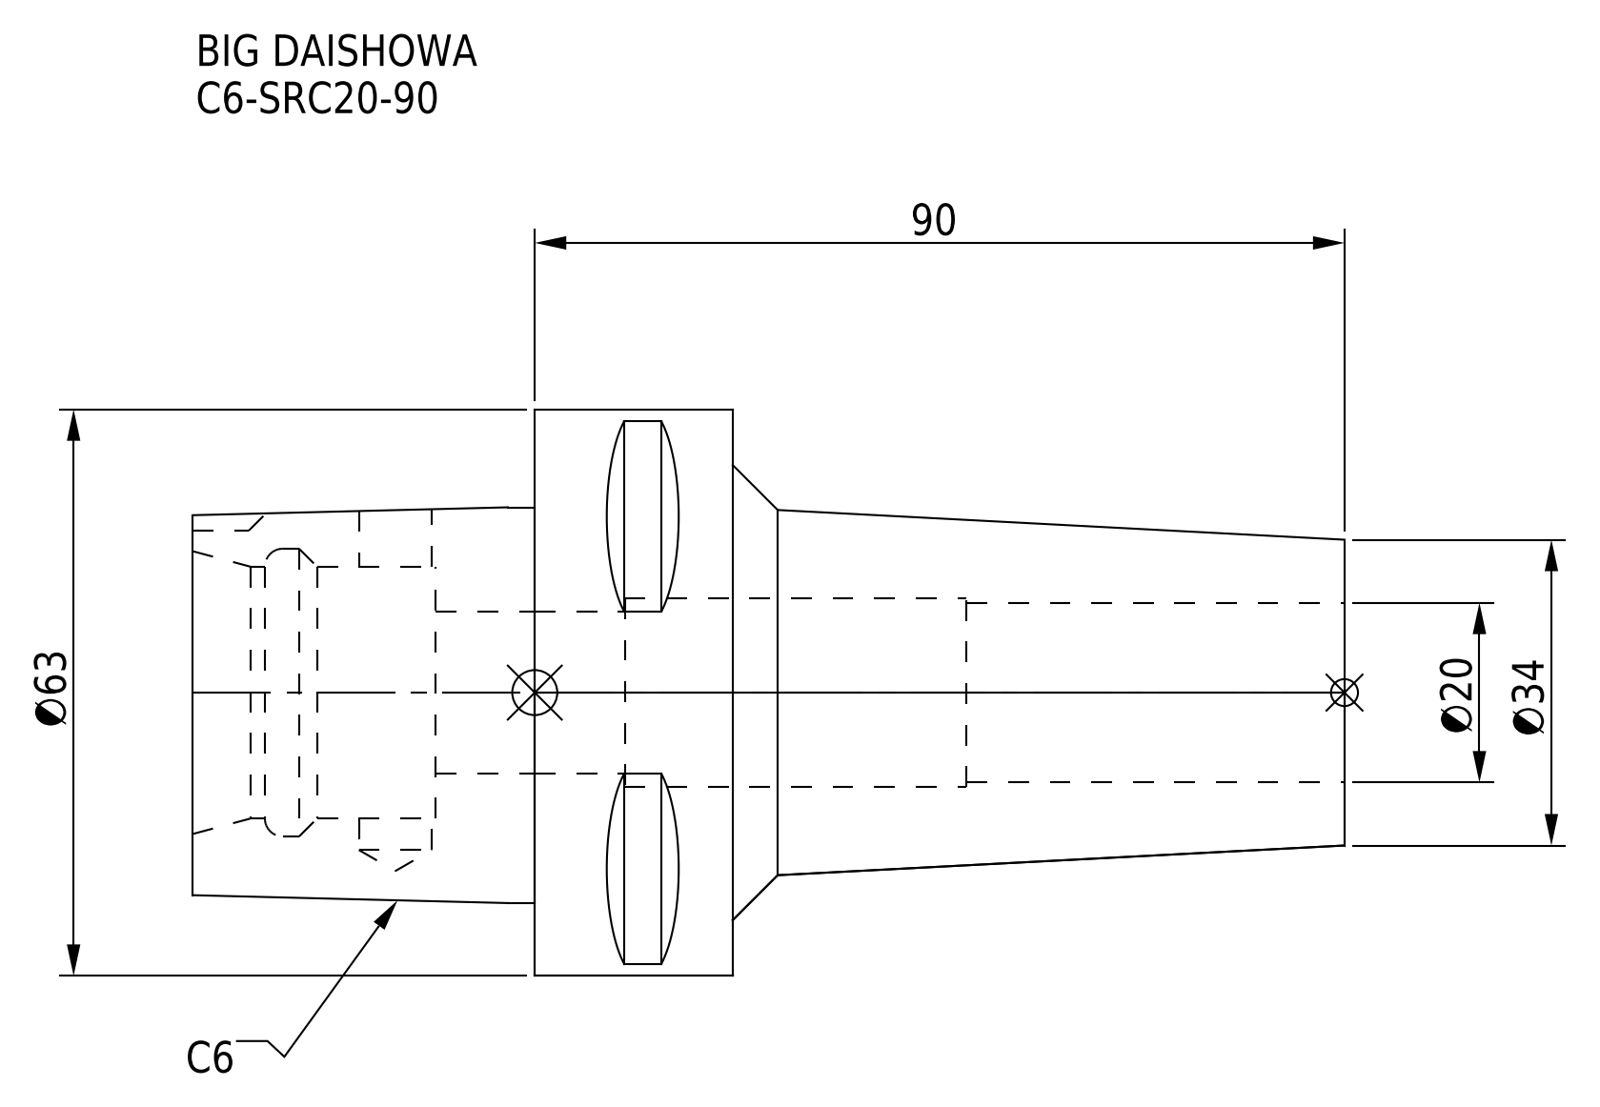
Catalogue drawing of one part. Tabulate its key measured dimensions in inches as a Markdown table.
| quantity | value |
| --- | --- |
| part name | C6-SRC20-90 |
| STEP written by | CREO PARAMETRIC BY PTC INC, 2016380 (AUTOMOTIVE_DESIGN) |
| units | inches |
| bodies | 1 solid, 62 faces (29 planar, 19 cylindrical, 14 other) |
| overall size | 5.039 × 2.48 × 2.48 |
| volume | 9.091 in³ |
| surface area | 49.31 in² |
| round holes (diameter × count) | 0.319 × 1, 0.709 × 1, 0.787 × 1, 0.827 × 1, 1.102 × 1, 1.26 × 1 |
| round bosses / shafts (diameter × count) | 2.48 × 1 |
| partial cylindrical surfaces (radius × count) | 0.197 × 1 |
| main face-to-face distances | 0.866, 2.677, 3.543, 1.496, 5.039, 2.362, 3.976, 1.299, 0.433, 1.063 |
